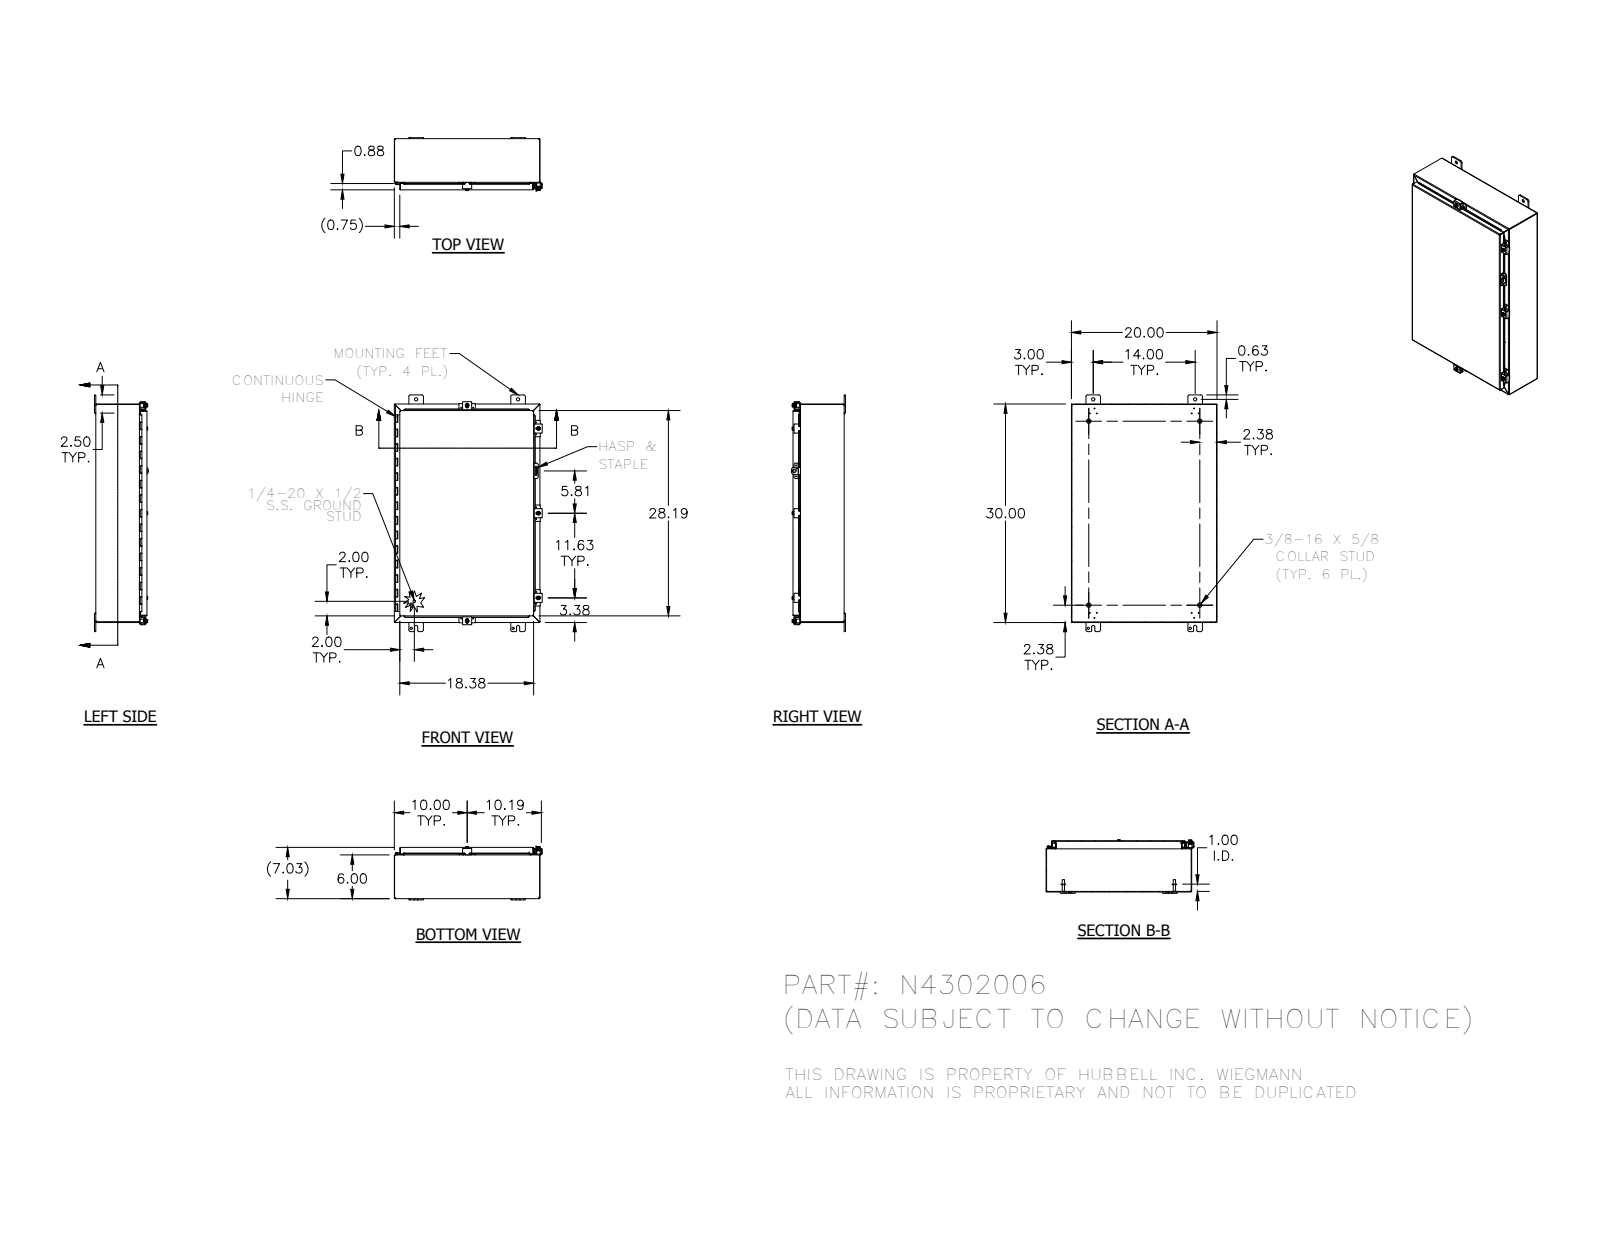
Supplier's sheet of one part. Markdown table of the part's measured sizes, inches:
| quantity | value |
| --- | --- |
| part name | 28x18_1; 34840_1; HFW30825-2_1; 30824_1 (+8 more) |
| STEP written by | SolidWorks 2014 (AUTOMOTIVE_DESIGN) |
| units | inches |
| bodies | 42 solids, 1923 faces (755 planar, 869 cylindrical, 299 other) |
| overall size | 32.5 × 20.311 × 7.41 |
| volume | 168.4 in³ |
| surface area | 4 392 in² |
| round holes (diameter × count) | 0.11 × 13, 0.12 × 12, 0.211 × 5, 0.281 × 5, 0.3 × 5, 0.313 × 4, 0.438 × 4, 0.125 × 1, 0.156 × 1, 0.5 × 1 |
| round bosses / shafts (diameter × count) | 0.25 × 7, 0.52 × 5, 0.5 × 5, 0.35 × 5, 0.625 × 4, 0.33 × 4, 0.115 × 2, 0.337 × 1 |
| partial cylindrical surfaces (radius × count) | 0.03 × 61, 0.125 × 35, 0.062 × 31, 0.25 × 31, 0.031 × 23, 0.105 × 23, 0.063 × 14, 0.141 × 10 |
| main face-to-face distances | 0.074, 6.959, 6.885, 7.033, 19.926, 5.926, 1.033, 29.926, 19.852, 20 |
| hole center spacings | 14, 0.876, 0.759, 0.839, 0.94, 0.969, 1.593, 1.995 |
